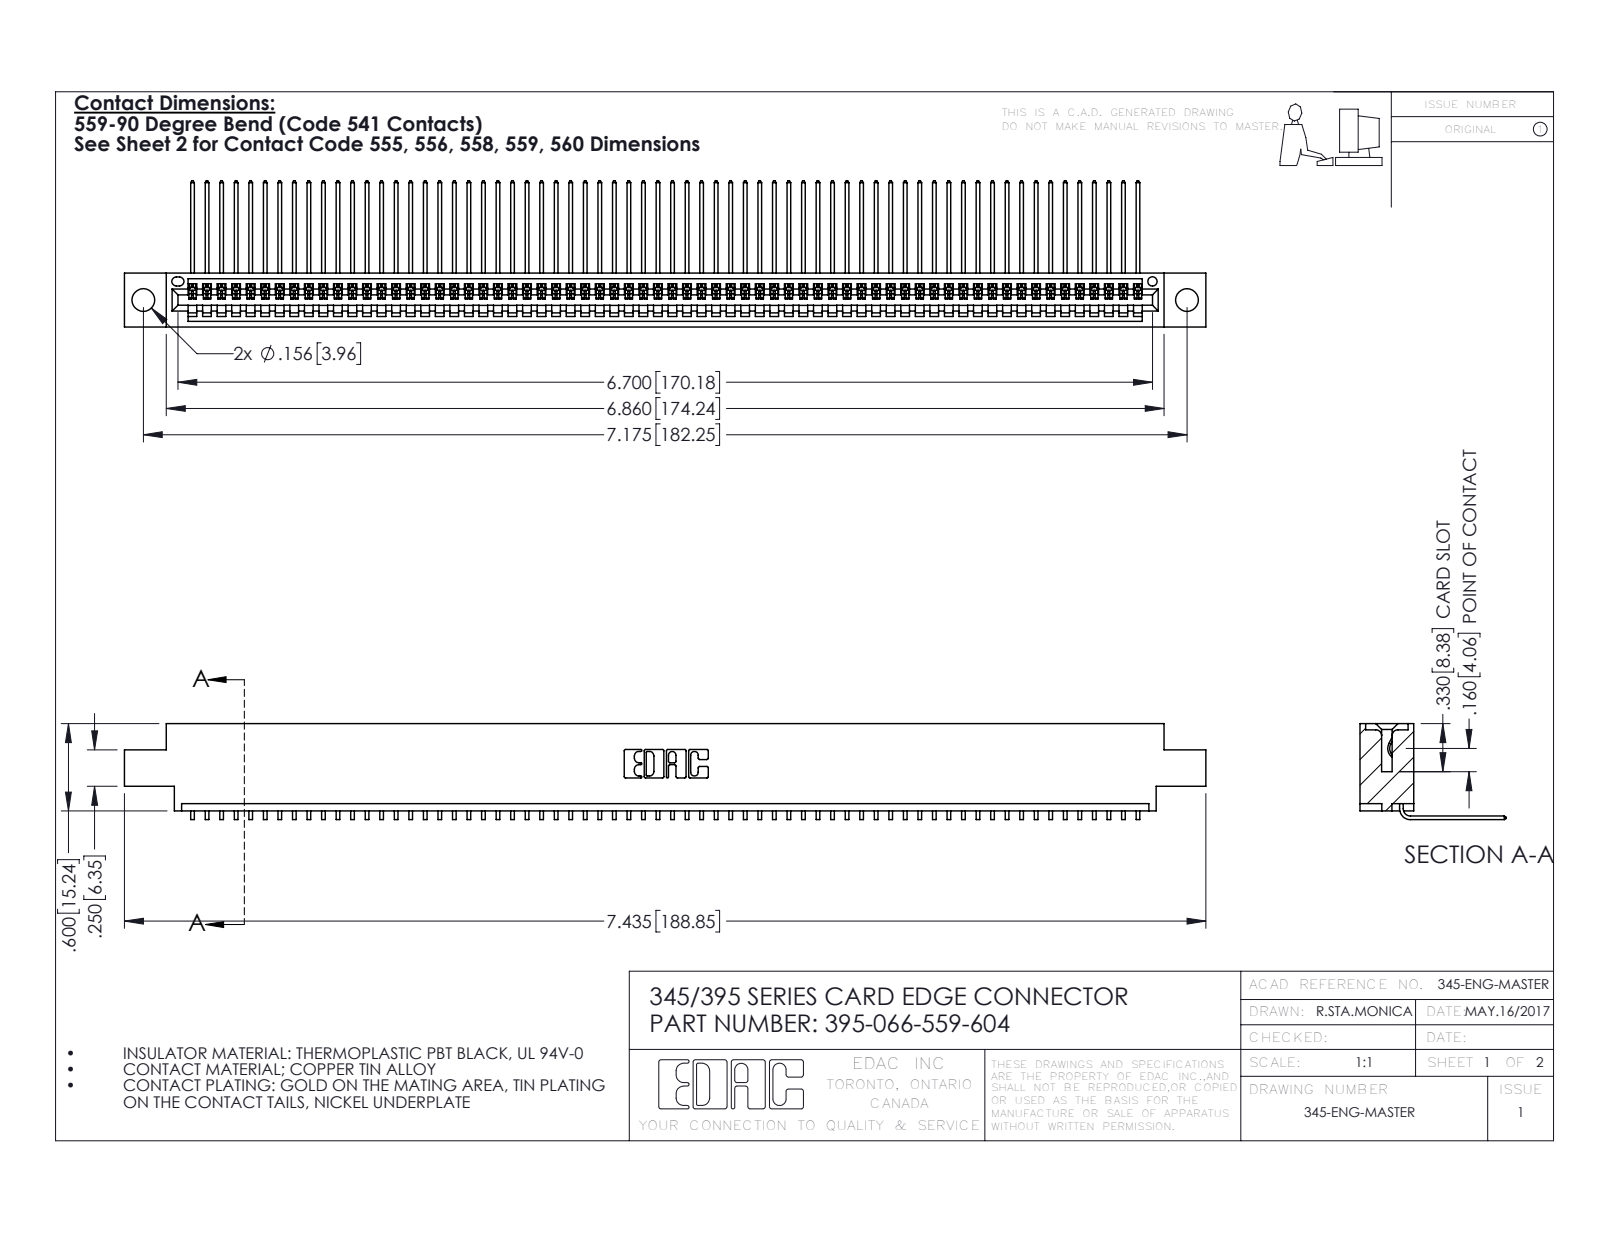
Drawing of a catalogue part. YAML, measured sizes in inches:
part_name: "345 Part_0.170 Offset - 0.156 Dia-TH; 345-292-001_558 559 Tail - 1; 395-066-559-604"
step_written_by: "SolidWorks 2016 (CONFIG_CONTROL_DESIGN)"
units: inches
bodies: {solids: 67, faces: 4090, planar: 2856, cylindrical: 1234, other: 0}
overall_size: [7.435, 1.005, 0.659]
volume: 1.108
surface_area: 39.8
round_holes:
  - {diameter: 0.156, count: 2}
  - {diameter: 0.064, count: 1}
partial_cylinders:
  - {radius: 0.006, count: 132}
  - {radius: 0.01, count: 22}
  - {radius: 0.007, count: 6}
  - {radius: 0.031, count: 6}
  - {radius: 0.026, count: 3}
  - {radius: 0.031, count: 2}
  - {radius: 0.04, count: 2}
  - {radius: 0.014, count: 1}
face_to_face_distances: [0.072, 0.298, 0.37, 0.2, 0.098, 0.272, 0.025, 0.225, 0.175, 0.149]
hole_center_spacings: [0.27, 6.939, 7.175]
